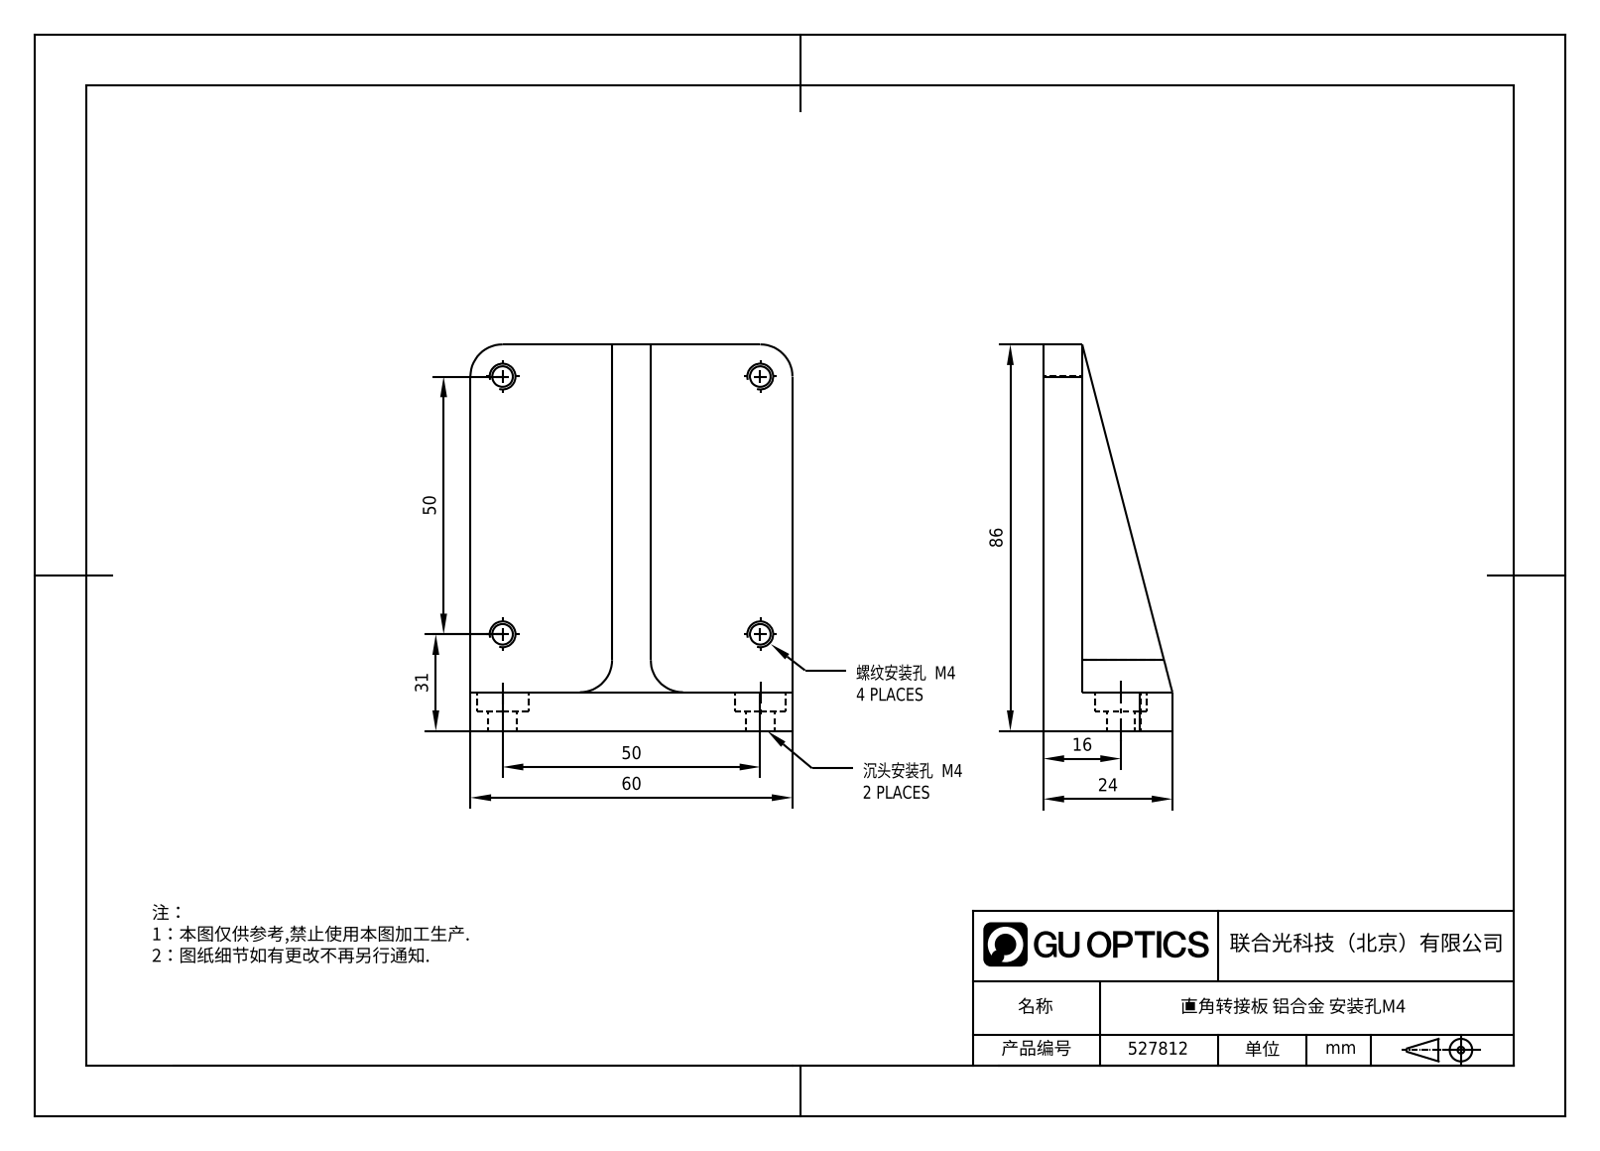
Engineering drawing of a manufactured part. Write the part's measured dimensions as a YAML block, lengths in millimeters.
part_name: "1.6.9.4_ZSJ-Z060_60mm直角转接板，带M4螺孔和M4沉头孔"
step_written_by: "SolidWorks 2021 (CONFIG_CONTROL_DESIGN)"
units: millimeters
bodies: {solids: 1, faces: 37, planar: 15, cylindrical: 22, other: 0}
overall_size: [86, 60, 24]
volume: 41219
surface_area: 15972
round_holes:
  - {diameter: 3.3, count: 4}
  - {diameter: 4.5, count: 2}
  - {diameter: 8, count: 2}
partial_cylinders:
  - {radius: 5, count: 6}
face_to_face_distances: [6, 27, 33, 60, 86, 80, 24, 18, 3, 83]
hole_center_spacings: [50, 70.71]
